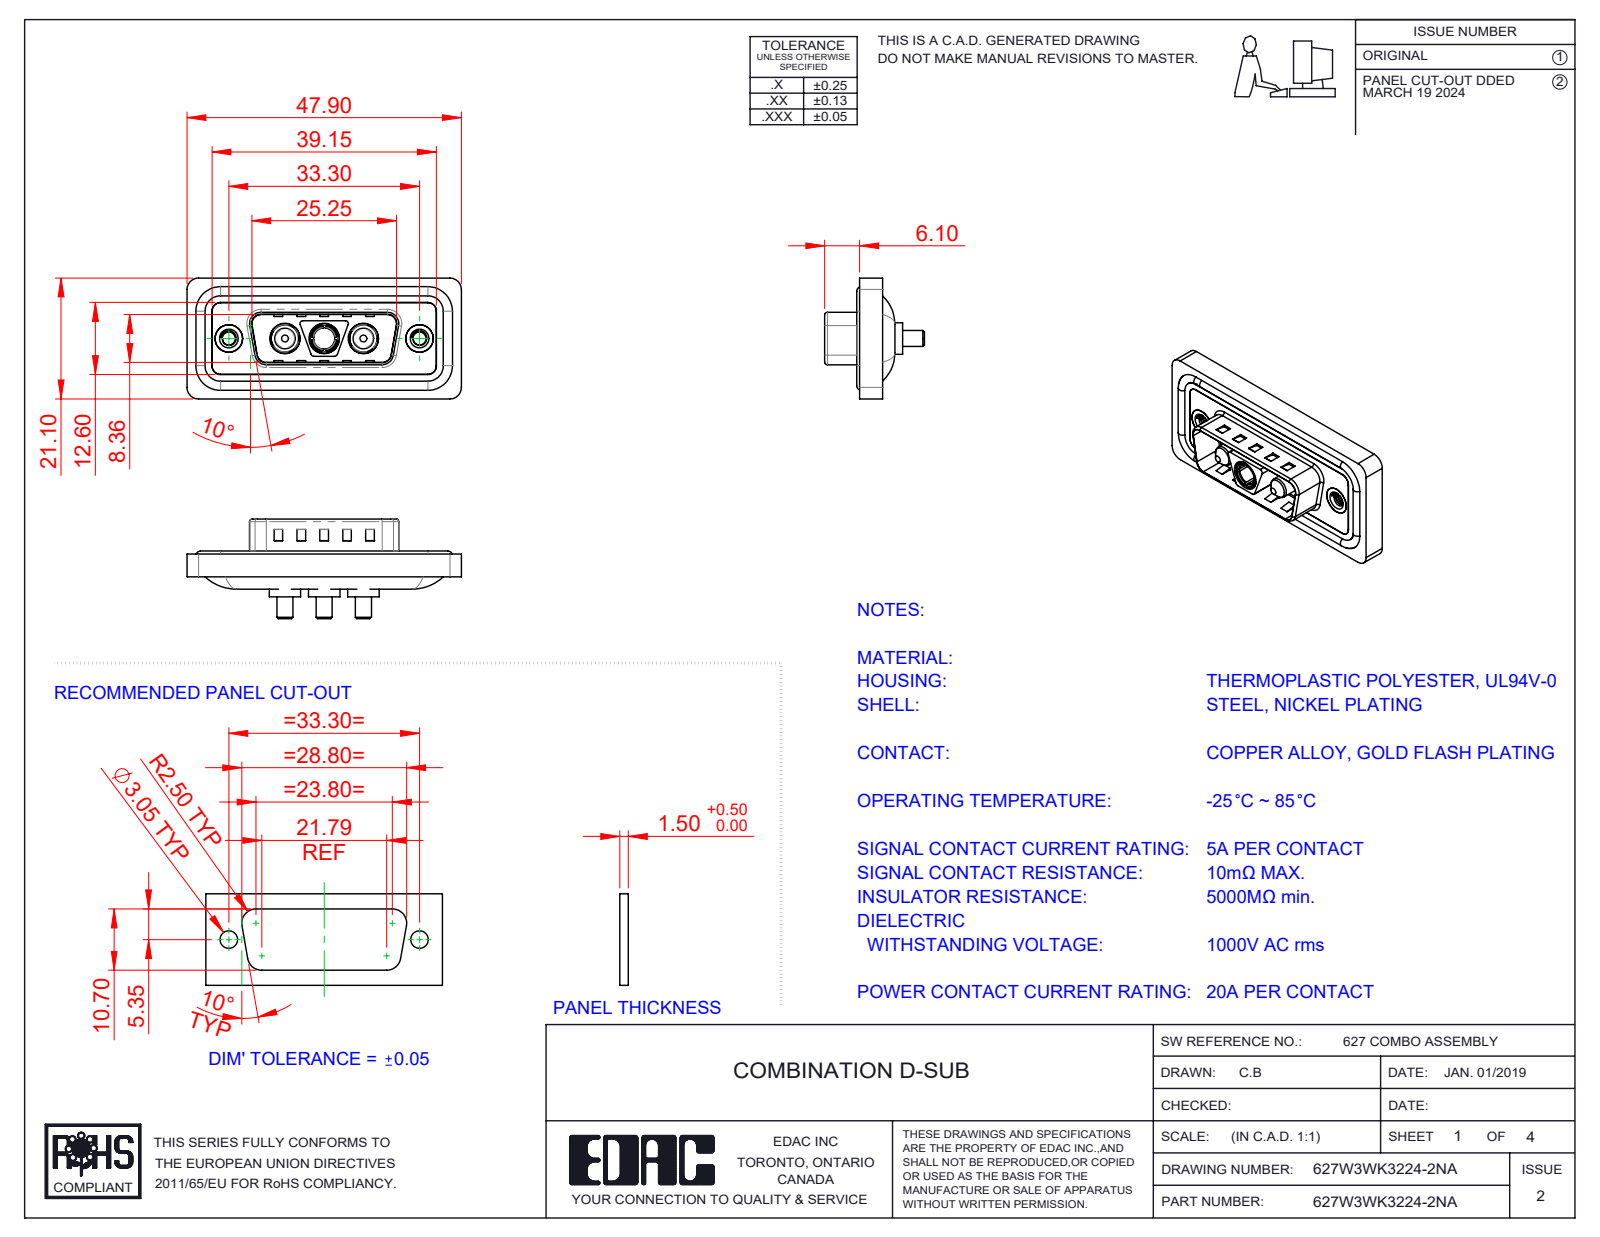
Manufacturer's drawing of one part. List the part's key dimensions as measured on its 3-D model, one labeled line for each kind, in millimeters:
Part name (STEP PRODUCT): Power Pin_20A S; 627Combo Threaded Rivet_A; 627W3WK3224-2NA; 627Combo Shell Rear_15 Contacts (+4 more)
STEP written by: SolidWorks 2023 (CONFIG_CONTROL_DESIGN)
Units: millimetres
Bodies: 13 solids, 607 faces (231 planar, 252 cylindrical, 124 other)
Overall size (bounding box): 47.9 × 21.1 × 17.4
Volume: 5 690 mm³ · Surface area: 9 125 mm²
Round holes (diameter × count): ⌀4.85 ×3, ⌀5.3 ×3, ⌀2.26 ×2, ⌀4 ×2, ⌀4.8 ×2, ⌀5 ×2, ⌀3.7 ×1
Round bosses / shafts (diameter × count): ⌀1.6 ×4, ⌀5.5 ×3, ⌀5.2 ×3, ⌀4.75 ×3, ⌀3.75 ×3, ⌀2.8 ×3, ⌀4.9 ×2, ⌀3.6 ×2
Partial cylindrical surfaces — rounded edges, fillets, slot ends (radius × count): R1.5 ×26, R2 ×20, R0.5 ×12, R1.6 ×8, R0.25 ×4, R0.6 ×4, R0.65 ×4, R0.9 ×4
Main face-to-face distances: 0.4, 1.1, 1.5, 0.5, 1.6, 3.1, 2.9, 4, 0.82, 9.58
Hole centre spacings: 6.85, 9.8, 16.65, 23.5, 13.7, 33.3
